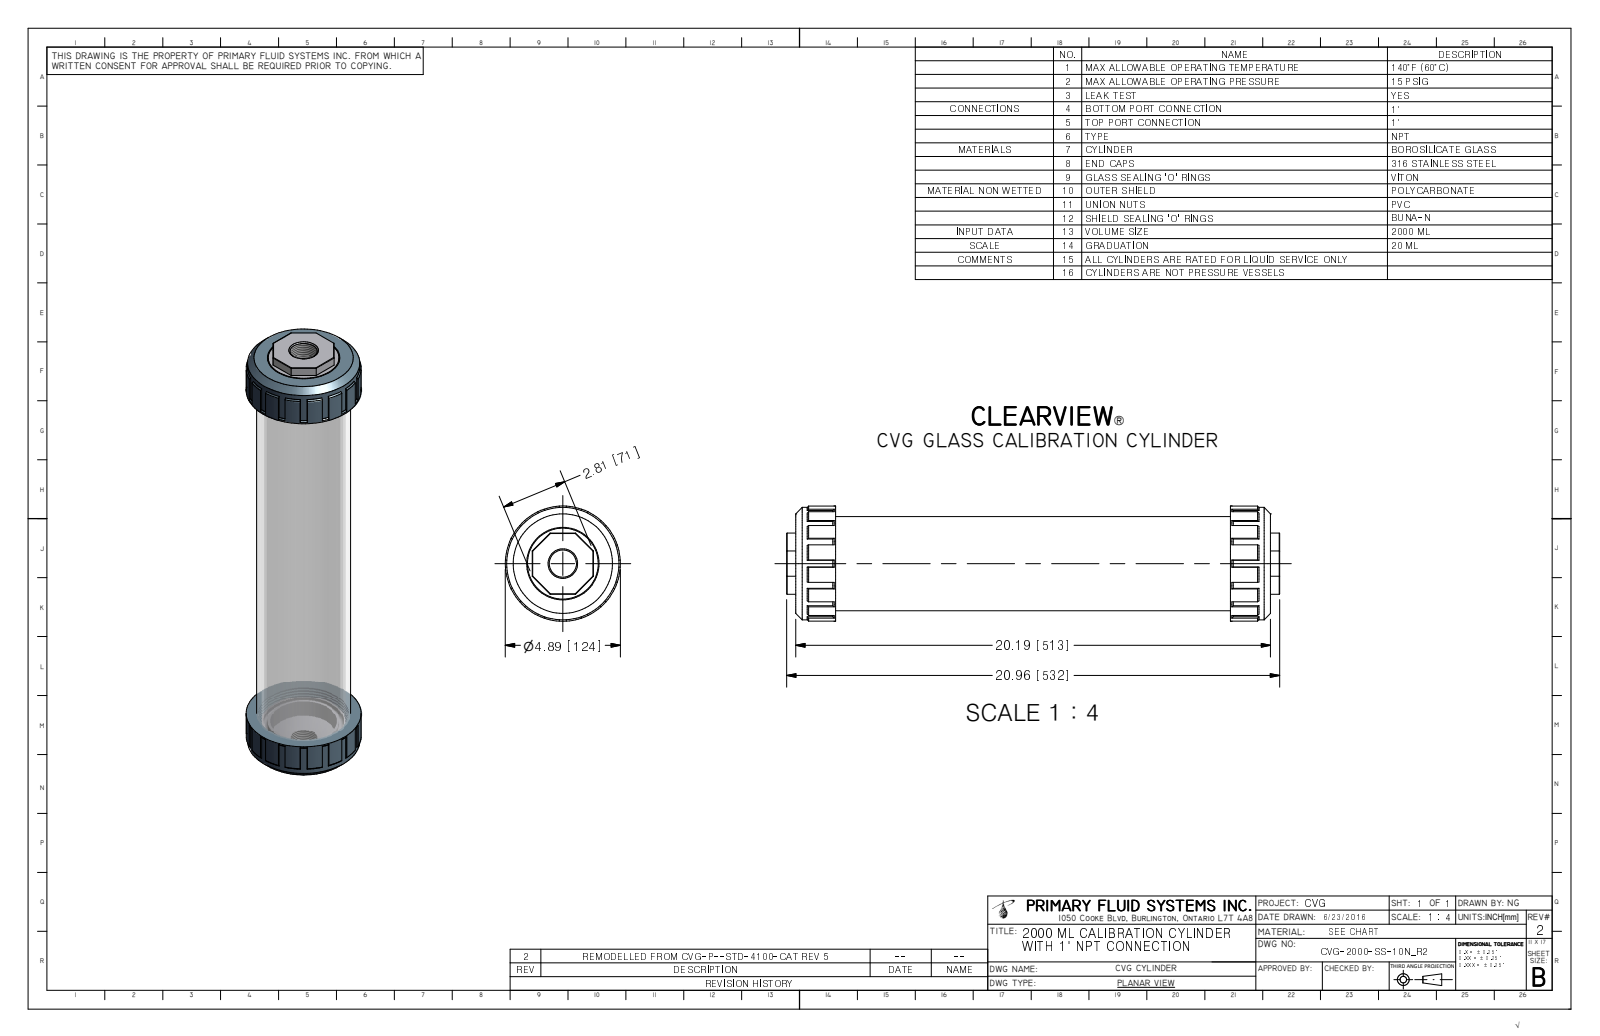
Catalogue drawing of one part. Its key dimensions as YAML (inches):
part_name: "CVG-2000-SS-10N_R2; CVG-3-2000-METAL-NPT-10_R4; CVG-1-2000-A_R0; CVG-6-2000 (+1 more)"
step_written_by: "Autodesk Inventor 2009 (AUTOMOTIVE_DESIGN)"
units: inches
bodies: {solids: 6, faces: 310, planar: 100, cylindrical: 64, other: 146}
overall_size: [20.96, 4.89, 4.89]
volume: 102.6
surface_area: 1089
round_holes:
  - {diameter: 1.156, count: 1}
  - {diameter: 2.825, count: 1}
  - {diameter: 3.075, count: 1}
  - {diameter: 3.15, count: 1}
  - {diameter: 3.4, count: 1}
  - {diameter: 3.58, count: 1}
  - {diameter: 3.819, count: 1}
  - {diameter: 3.945, count: 1}
  - {diameter: 3.945, count: 1}
round_bosses_or_shafts:
  - {diameter: 4.89, count: 1}
  - {diameter: 4.77, count: 1}
  - {diameter: 4, count: 1}
  - {diameter: 3.74, count: 1}
  - {diameter: 3.55, count: 1}
  - {diameter: 3.412, count: 1}
  - {diameter: 3.346, count: 1}
  - {diameter: 3.025, count: 1}
face_to_face_distances: [1.7, 18.488, 0.386, 2.086, 18.874, 20.574, 20.188, 16.788, 19.238, 0.686]
